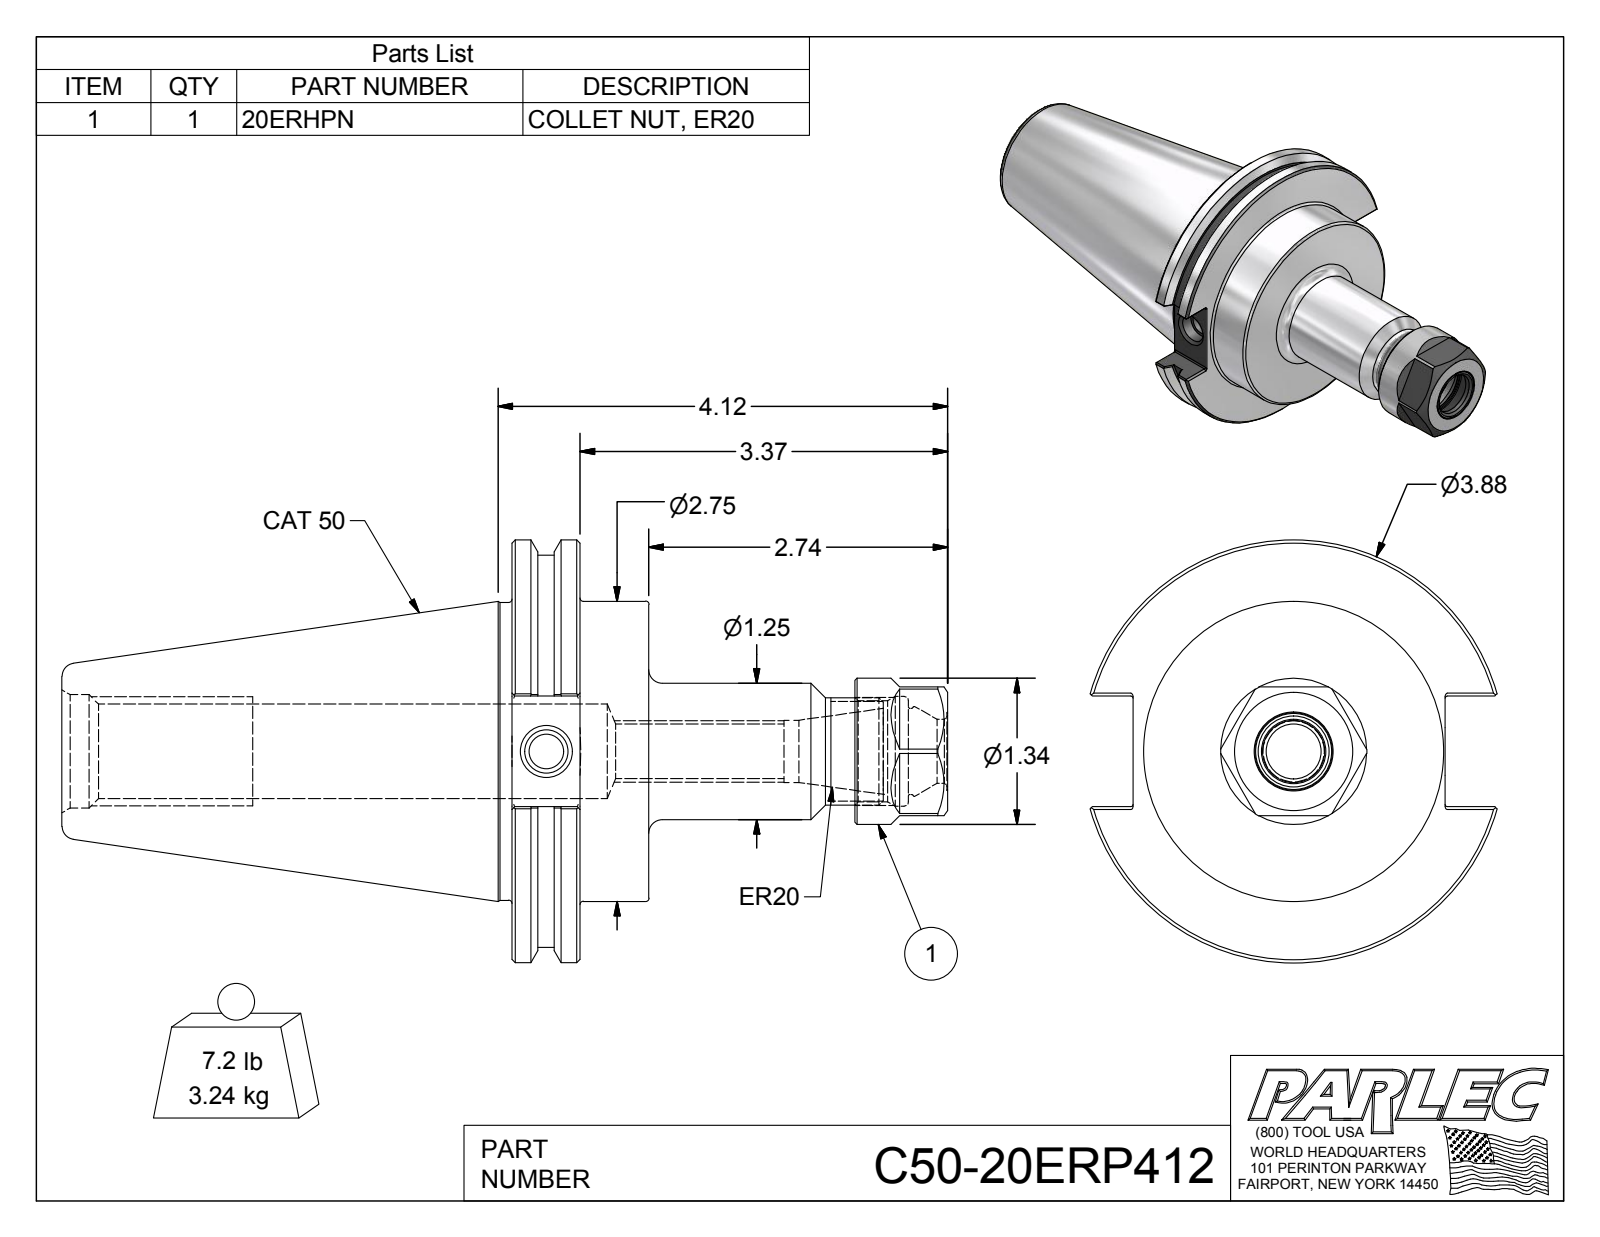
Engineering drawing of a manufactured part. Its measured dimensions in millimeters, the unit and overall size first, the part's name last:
Units: millimetres
Overall size (bounding box): 206.2 × 98.4 × 94.7
Round holes (diameter × count): ⌀8 ×1, ⌀10.1 ×1, ⌀12.8 ×1, ⌀14.5 ×1, ⌀14.9 ×1, ⌀20.1 ×1, ⌀22 ×1, ⌀23.5 ×1, ⌀25.5 ×1, ⌀26.4 ×1
Round bosses / shafts (diameter × count): ⌀98.4 ×1, ⌀91.3 ×1, ⌀69.9 ×1, ⌀69.3 ×1, ⌀34 ×1, ⌀31.8 ×1, ⌀25 ×1
Partial cylindrical surfaces — rounded edges, fillets, slot ends (radius × count): R0.5 ×12
Main face-to-face distances: 15.9, 31.9, 16, 30, 79.9, 64, 48, 101.5, 85.6, 69.6
Volume: 414 400 mm³ · Surface area: 60 540 mm²
Bodies: 2 solids, 126 faces (49 planar, 33 cylindrical, 44 other)
Part name (STEP PRODUCT): C50-20ERP412; C50-20ER4-1; 20ERHPN
STEP written by: Autodesk Inventor 2012 (AUTOMOTIVE_DESIGN)
